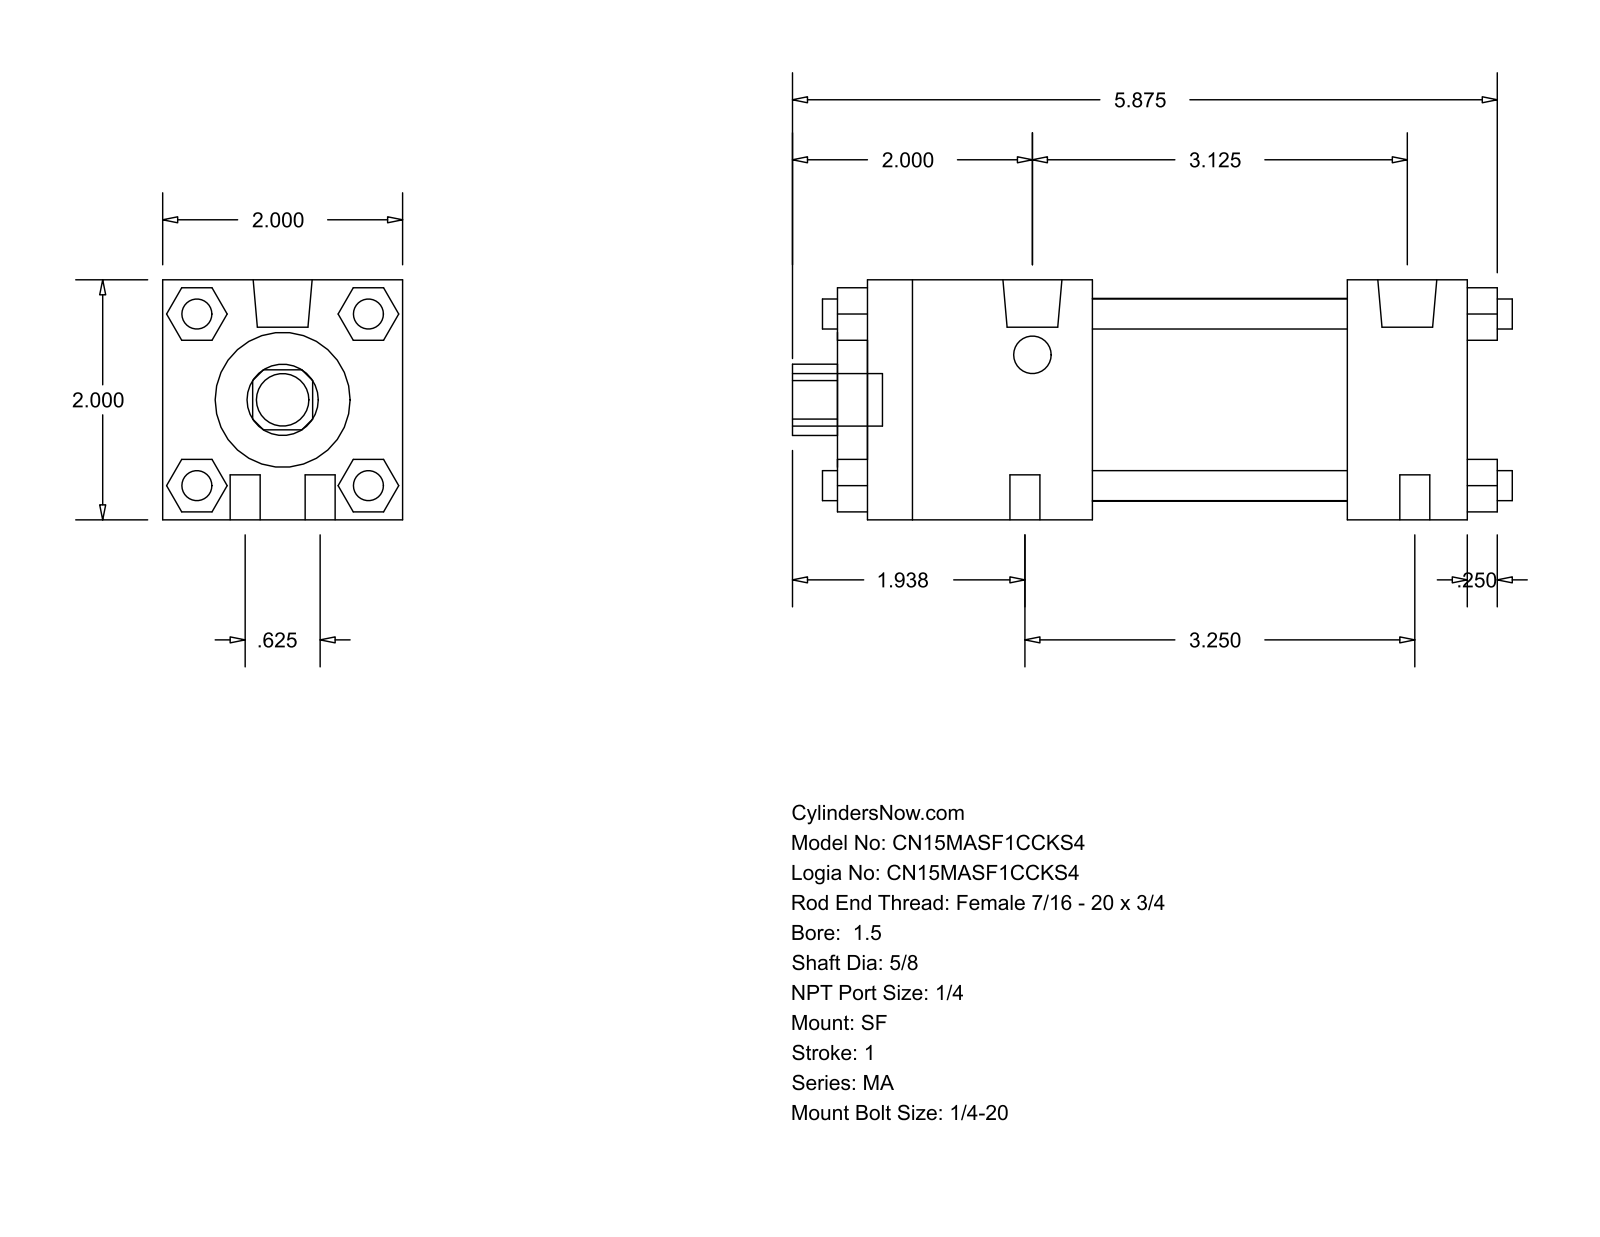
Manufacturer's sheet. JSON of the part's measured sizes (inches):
{"part_name": "MA_SF__0150_0.625", "step_written_by": "GSSL Pune (CONFIG_CONTROL_DESIGN)", "units": "inches", "bodies": {"solids": 0, "faces": 124, "planar": 94, "cylindrical": 30, "other": 0}, "overall_size": [6, 2, 2], "round_holes": [[0.625, 1], [1.125, 1], [1.69, 1]], "round_bosses_or_shafts": [[0.25, 8], [0.492, 2], [0.313, 2], [0.437, 1]], "partial_cylinders_radius": [[0.297, 1]], "face_to_face_distances": [2, 2.125, 5, 1.875, 4, 3.125, 1, 0.25, 5.25, 4.25]}
